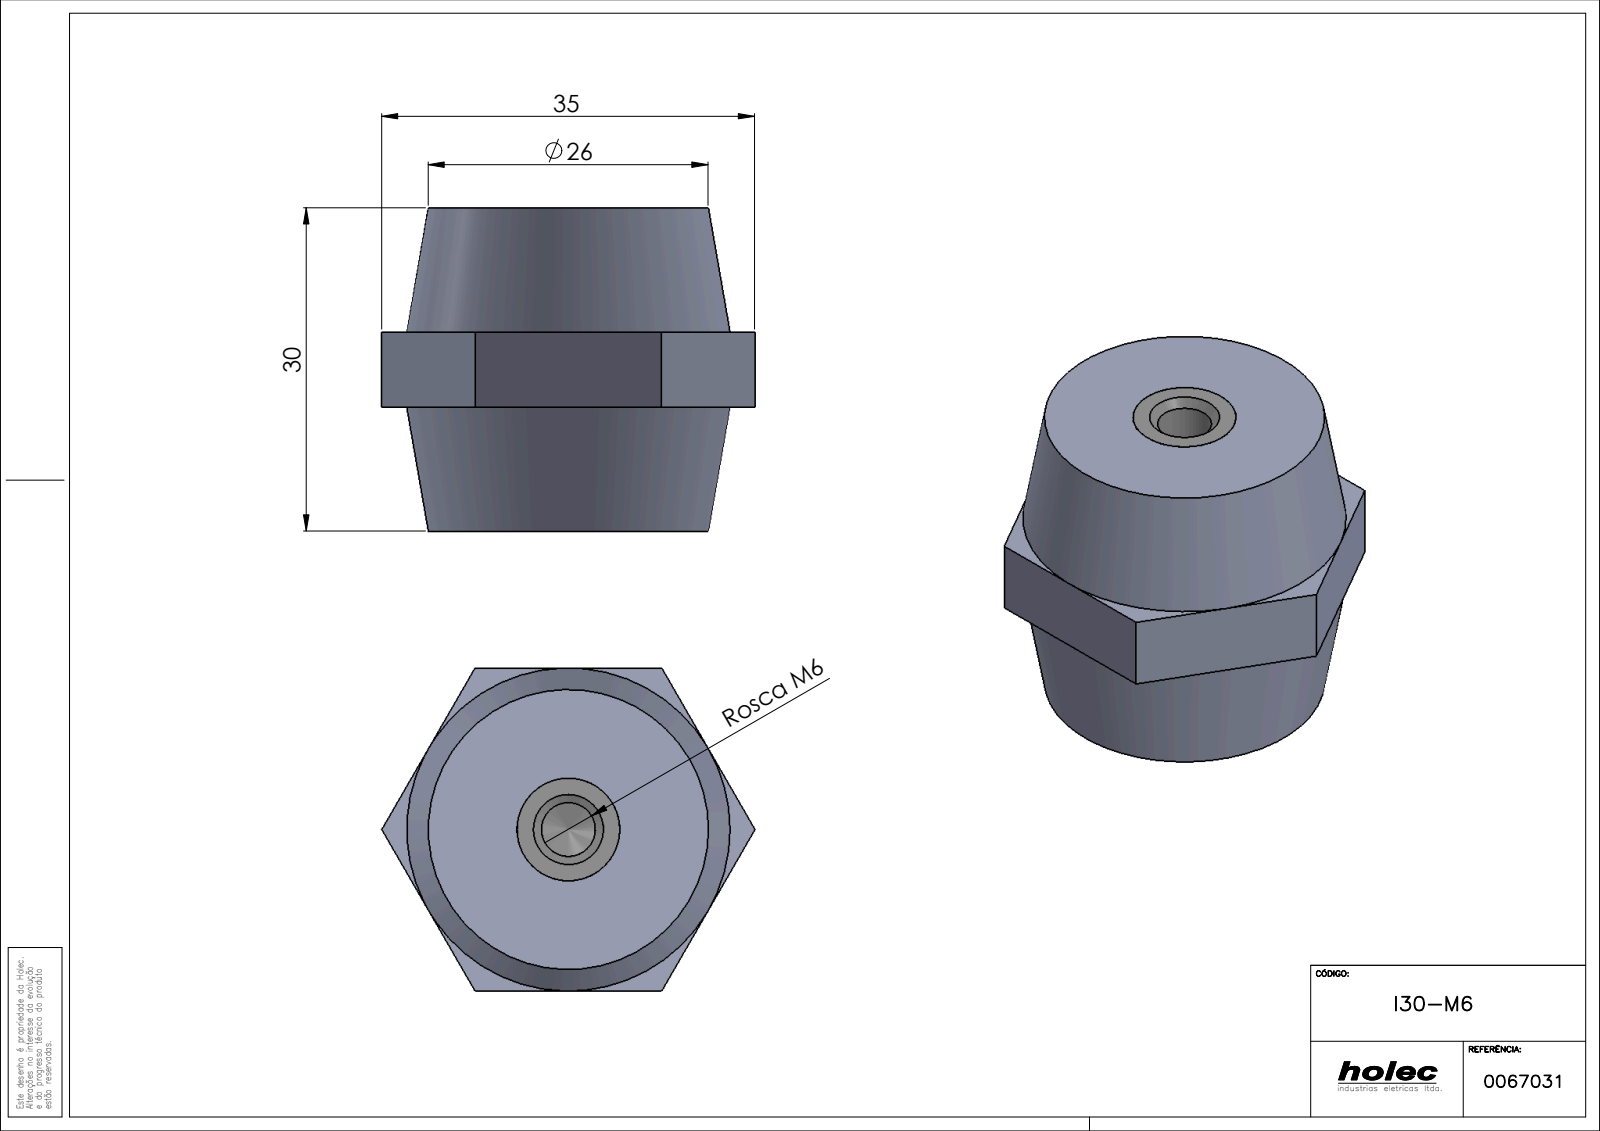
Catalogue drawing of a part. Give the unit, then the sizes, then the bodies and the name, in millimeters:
Units: millimetres
Overall size (bounding box): 34.64 × 30 × 30
Round holes (diameter × count): ⌀5 ×1, ⌀8 ×1
Main face-to-face distances: 30, 9.52, 22.01, 22, 2.5, 5.5, 11.5, 18.5, 7.99, 8
Volume: 19 379 mm³ · Surface area: 5 658 mm²
Bodies: 3 solids, 162 faces (82 planar, 12 cylindrical, 68 other)
Part name (STEP PRODUCT): I30-M6; PB1_0000; PB1_0102(PB1_0102_06)
STEP written by: SolidWorks 2017 (AUTOMOTIVE_DESIGN)
